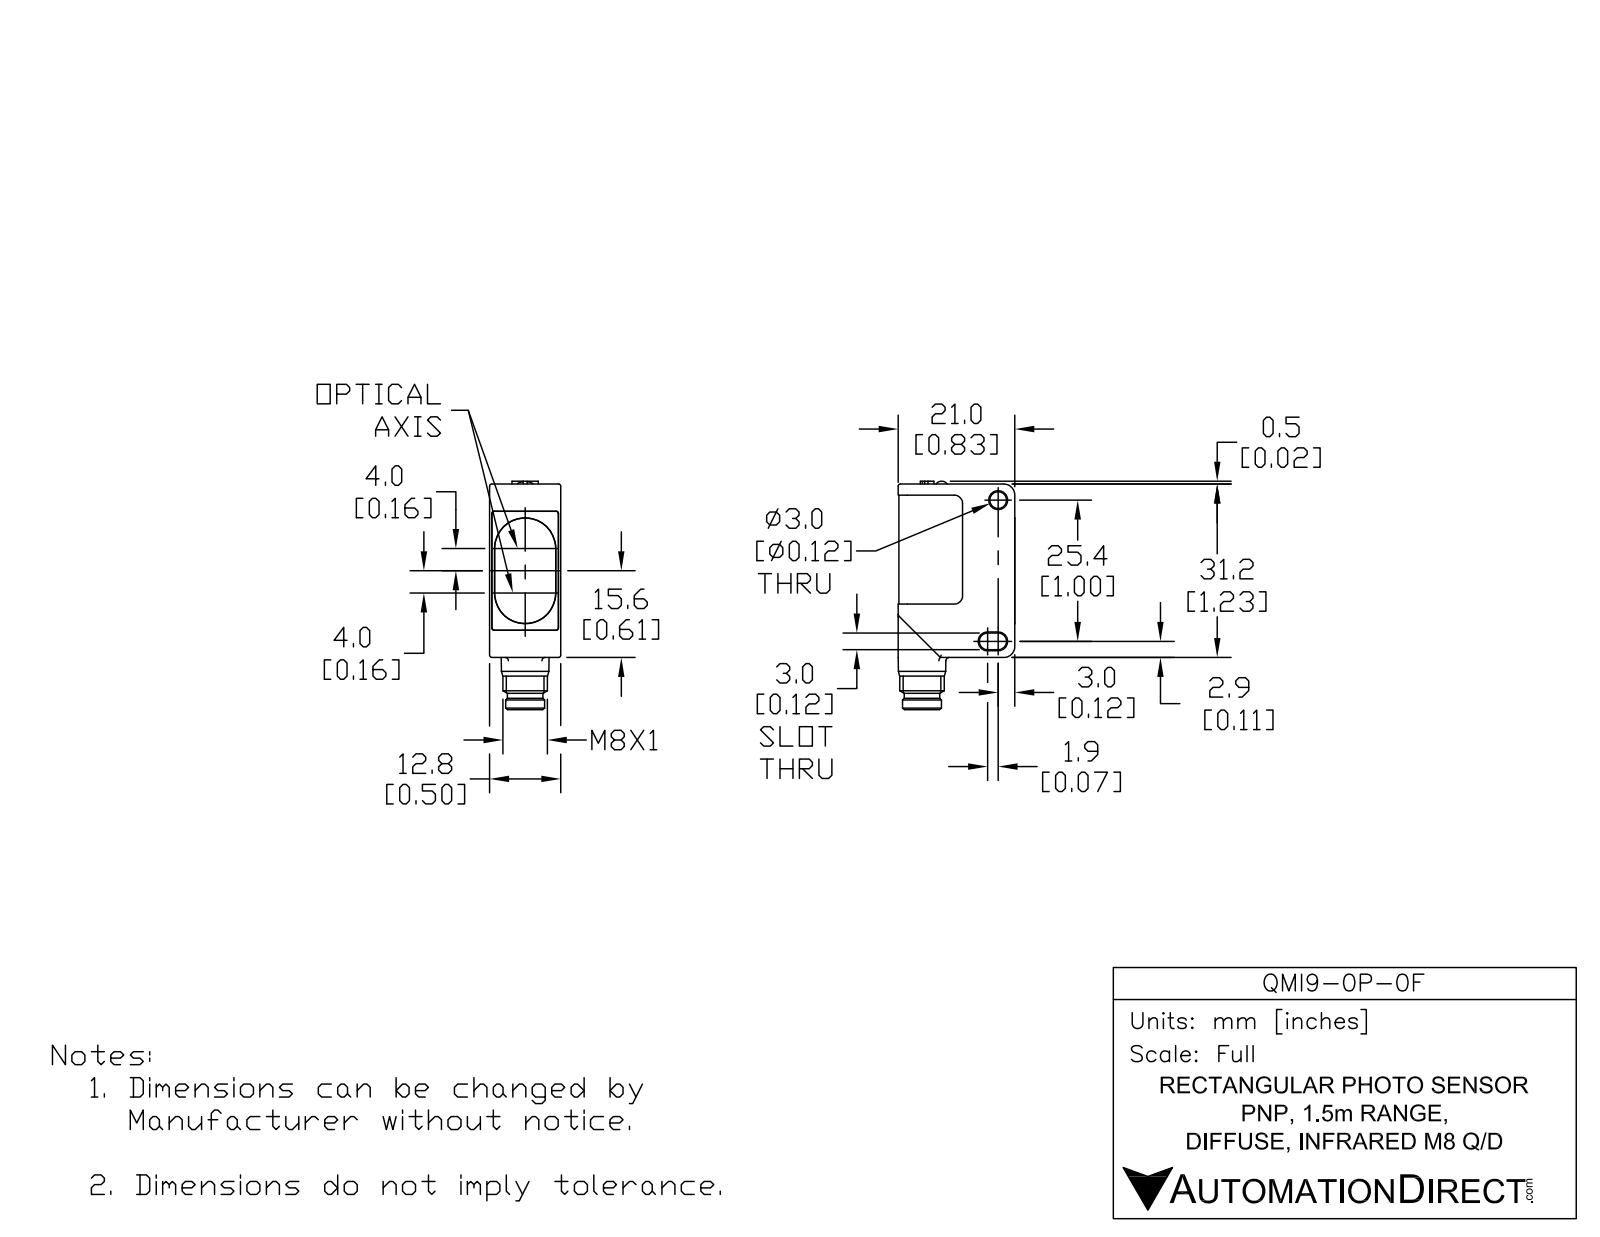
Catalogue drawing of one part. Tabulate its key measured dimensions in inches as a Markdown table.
| quantity | value |
| --- | --- |
| part name | QMI9-0P-0F |
| STEP written by | SolidWorks 2017 (AUTOMOTIVE_DESIGN) |
| units | inches |
| bodies | 7 solids, 272 faces (125 planar, 100 cylindrical, 47 other) |
| overall size | 1.619 × 0.827 × 0.504 |
| volume | 0.474 in³ |
| surface area | 7.749 in² |
| round holes (diameter × count) | 0.118 × 3, 0.228 × 1 |
| round bosses / shafts (diameter × count) | 0.039 × 4, 0.138 × 2, 0.315 × 1, 0.276 × 1, 0.252 × 1 |
| partial cylindrical surfaces (radius × count) | 0.016 × 10, 0.02 × 9, 0.059 × 6, 0.024 × 4, 0.039 × 4, 0.006 × 2, 0.044 × 2, 0.065 × 2 |
| main face-to-face distances | 0.498, 0.02, 0.504, 0.11, 0.016, 0.492, 0.488, 0.482, 0.059, 0.711 |
| hole center spacings | 0.04, 0.205, 0.245 |
